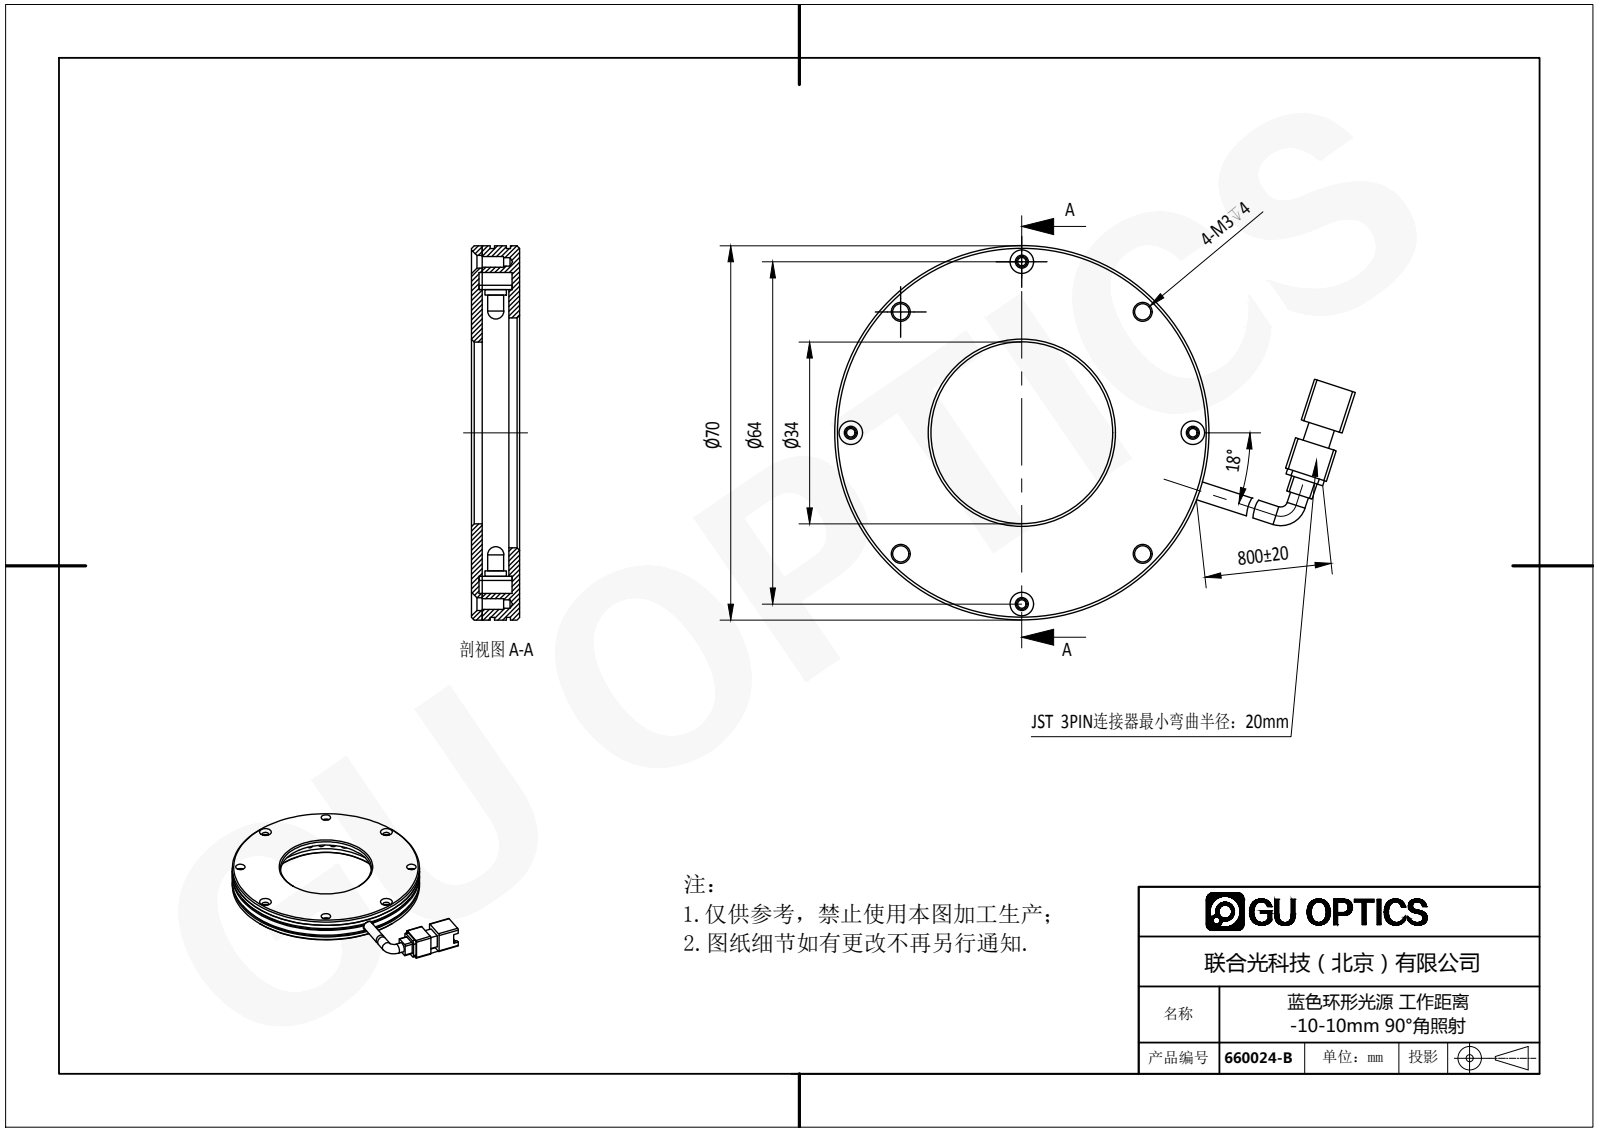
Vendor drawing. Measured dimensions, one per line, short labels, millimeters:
name: 660024-B
written by: SolidWorks 2016 (AUTOMOTIVE_DESIGN)
unit: mm
bodies: 37 solids, 771 faces (464 planar, 242 cylindrical, 65 other)
size: 97.4 × 70 × 11
volume: 17 278 mm³; area: 21 297 mm²
holes: 4× ⌀1.6, 4× ⌀2, 4× ⌀2.4, 4× ⌀3, 4× ⌀3.5, 1× ⌀3.6, 1× ⌀3.8, 1× ⌀34, 1× ⌀43, 1× ⌀54, 1× ⌀60
bosses: 32× ⌀3, 31× ⌀3.8, 2× ⌀3.5, 1× ⌀70, 1× ⌀69, 1× ⌀54.8, 1× ⌀53.6
rounds: 8× R0.5, 4× R1, 2× R1.5, 1× R33
face distances: 2, 7, 9, 0.6, 7.6, 5.6, 1.4, 5, 6.2, 1
hole spacings: 24.49, 32, 59.13, 45.25, 45.26, 64, 64.01
